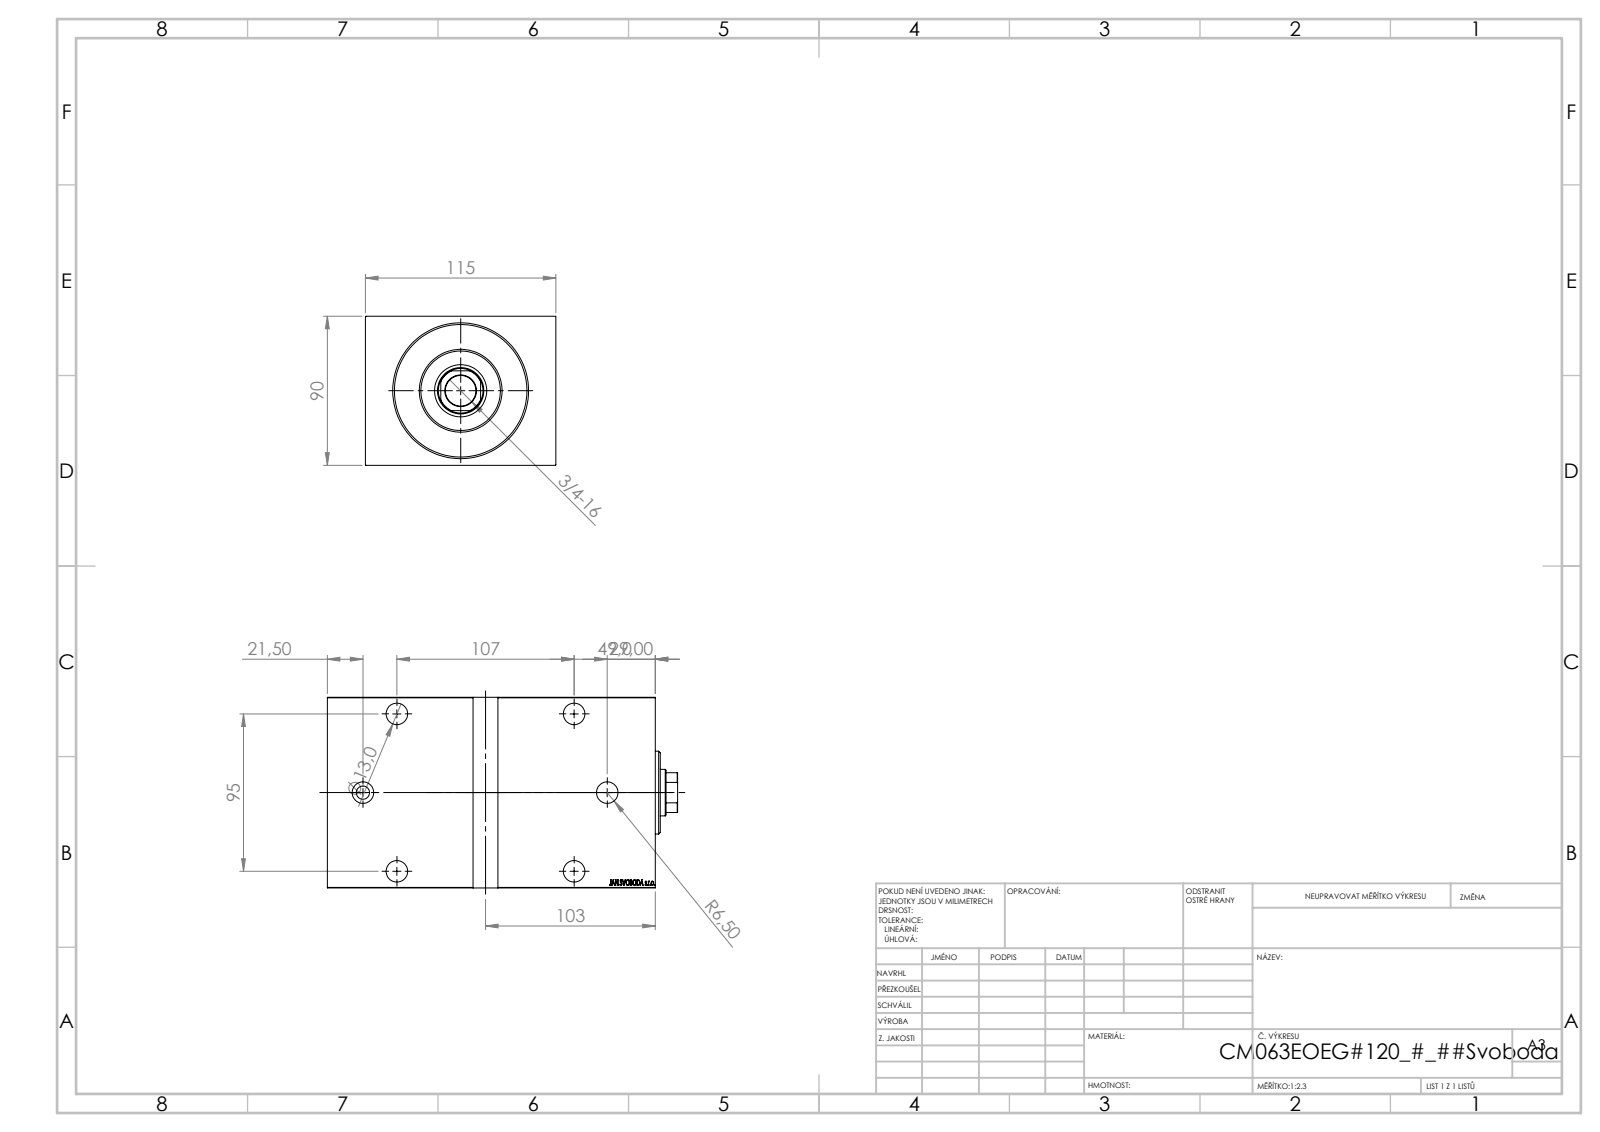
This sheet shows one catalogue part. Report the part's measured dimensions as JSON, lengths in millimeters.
{"part_name": "V450CM_E_Body; V450CM_E_VCP; V450CM_VC_B", "step_written_by": "SolidWorks 2019 (CONFIG_CONTROL_DESIGN)", "units": "millimeters", "bodies": {"solids": 3, "faces": 849, "planar": 409, "cylindrical": 46, "other": 394}, "overall_size": [211.5, 115, 90], "volume_mm3": 1692000, "surface_area_mm2": 198745, "round_holes": [[13, 6], [19, 4], [18.5, 1], [28, 1], [31.5, 1], [63, 1], [80, 1]], "round_bosses_or_shafts": [[65, 1], [50, 1], [8, 1]], "partial_cylinders_radius": [[13.5, 1]], "face_to_face_distances": [90, 115, 198, 17.5, 180.5, 5, 193, 175.5, 181.4, 163.9], "hole_center_spacings": [51.54, 51.73, 95, 107, 135.59, 136.06, 143.09, 147.5]}
